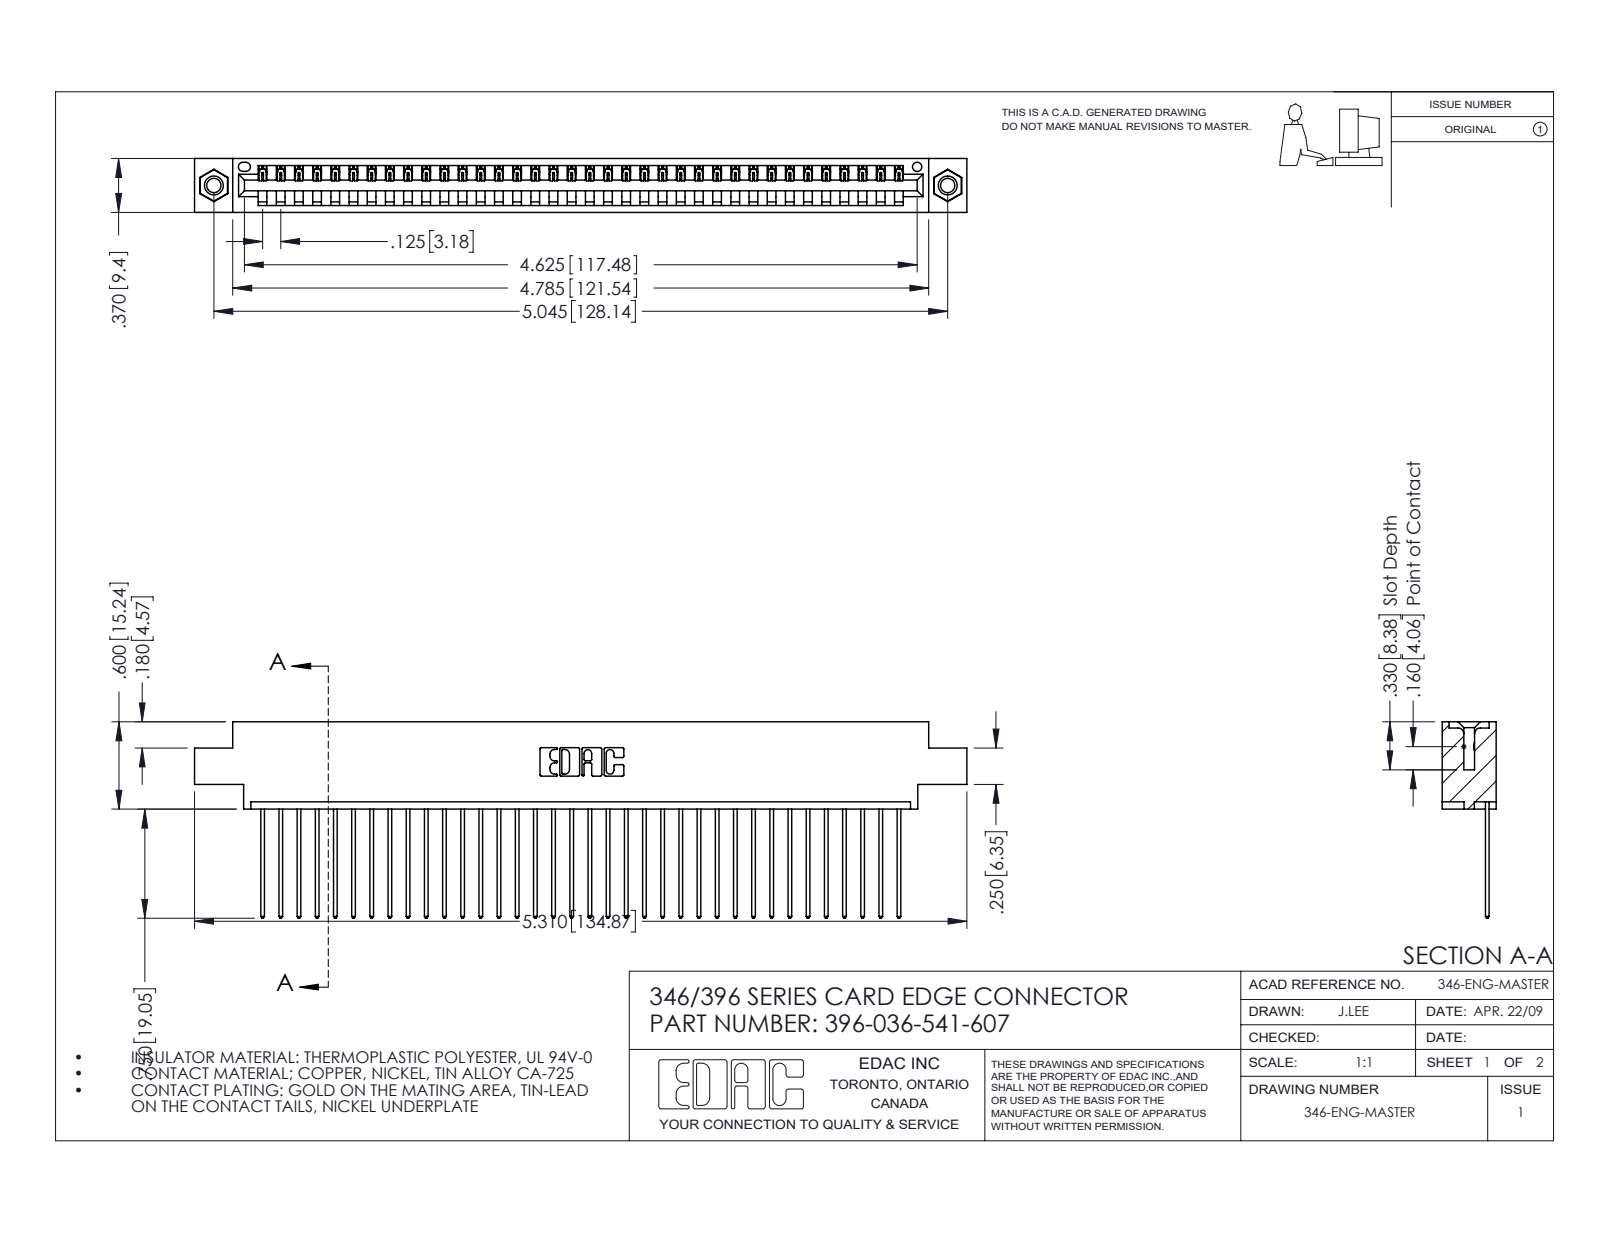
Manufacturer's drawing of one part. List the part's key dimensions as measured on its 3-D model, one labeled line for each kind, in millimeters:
Part name (STEP PRODUCT): 346 Part_0.170 Offset - 0.156 Dia-TI; 396-036-541-607; 345-292-001_345-293-141; 345-250-001_345-250-005-103
STEP written by: SolidWorks 2016 (CONFIG_CONTROL_DESIGN)
Units: millimetres
Bodies: 39 solids, 2274 faces (1552 planar, 706 cylindrical, 16 other)
Overall size (bounding box): 134.9 × 34.3 × 9.4
Volume: 12 800 mm³ · Surface area: 16 860 mm²
Round holes (diameter × count): ⌀2.5 ×2, ⌀3.2 ×2, ⌀4 ×2, ⌀1.6 ×1
Round bosses / shafts (diameter × count): ⌀3.9 ×2
Partial cylindrical surfaces — rounded edges, fillets, slot ends (radius × count): R0.2 ×72, R0.3 ×72, R0.3 ×22, R0.2 ×6, R0.8 ×6, R0.7 ×3, R0.8 ×2, R1 ×2
Main face-to-face distances: 1.2, 8.2, 9.4, 6.4, 1.8, 7.6, 0.6, 5.6, 3.8, 2.5
Hole centre spacings: 6.2, 122.8, 128.1
